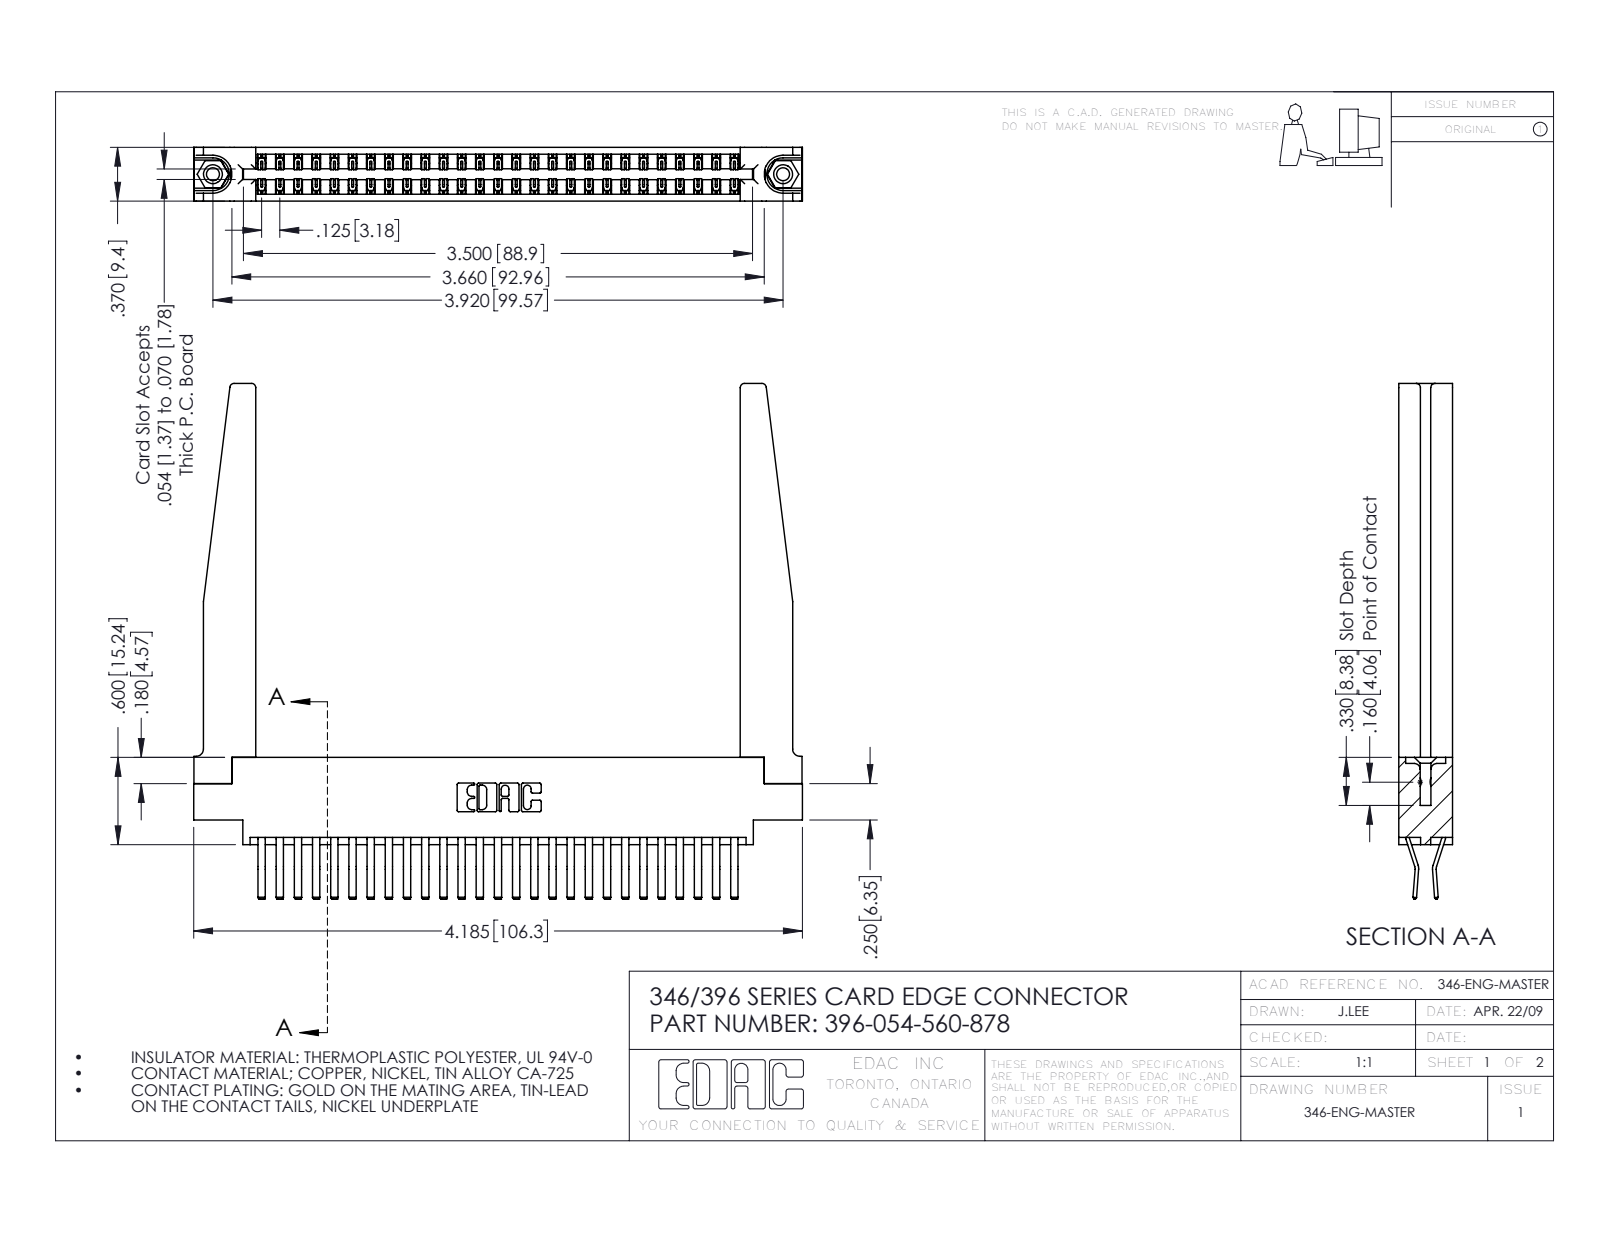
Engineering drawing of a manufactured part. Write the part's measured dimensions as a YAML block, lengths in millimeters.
part_name: "345-292-001_560 Tail; 396-054-560-878; 345-250-001_345-250-001-102; 346 Part_0.170 Offset - 0.156 Dia-TH (+1 more)"
step_written_by: "SolidWorks 2016 (CONFIG_CONTROL_DESIGN)"
units: millimeters
bodies: {solids: 59, faces: 3276, planar: 2112, cylindrical: 1112, other: 52}
overall_size: [106.3, 90, 9.4]
volume: 17350
surface_area: 21790
round_holes:
  - {diameter: 2.3, count: 2}
  - {diameter: 3.2, count: 2}
  - {diameter: 4, count: 2}
  - {diameter: 1.6, count: 1}
round_bosses_or_shafts:
  - {diameter: 3.9, count: 2}
partial_cylinders:
  - {radius: 0.2, count: 81}
  - {radius: 0.3, count: 22}
  - {radius: 0.8, count: 8}
  - {radius: 0.2, count: 6}
  - {radius: 0.8, count: 6}
  - {radius: 1.3, count: 4}
  - {radius: 0.7, count: 3}
  - {radius: 0.3, count: 2}
face_to_face_distances: [9.4, 1.2, 8.2, 1.8, 3.8, 3.8, 0.6, 6.4, 7.6, 7]
hole_center_spacings: [6.2, 94.3, 99.6]
